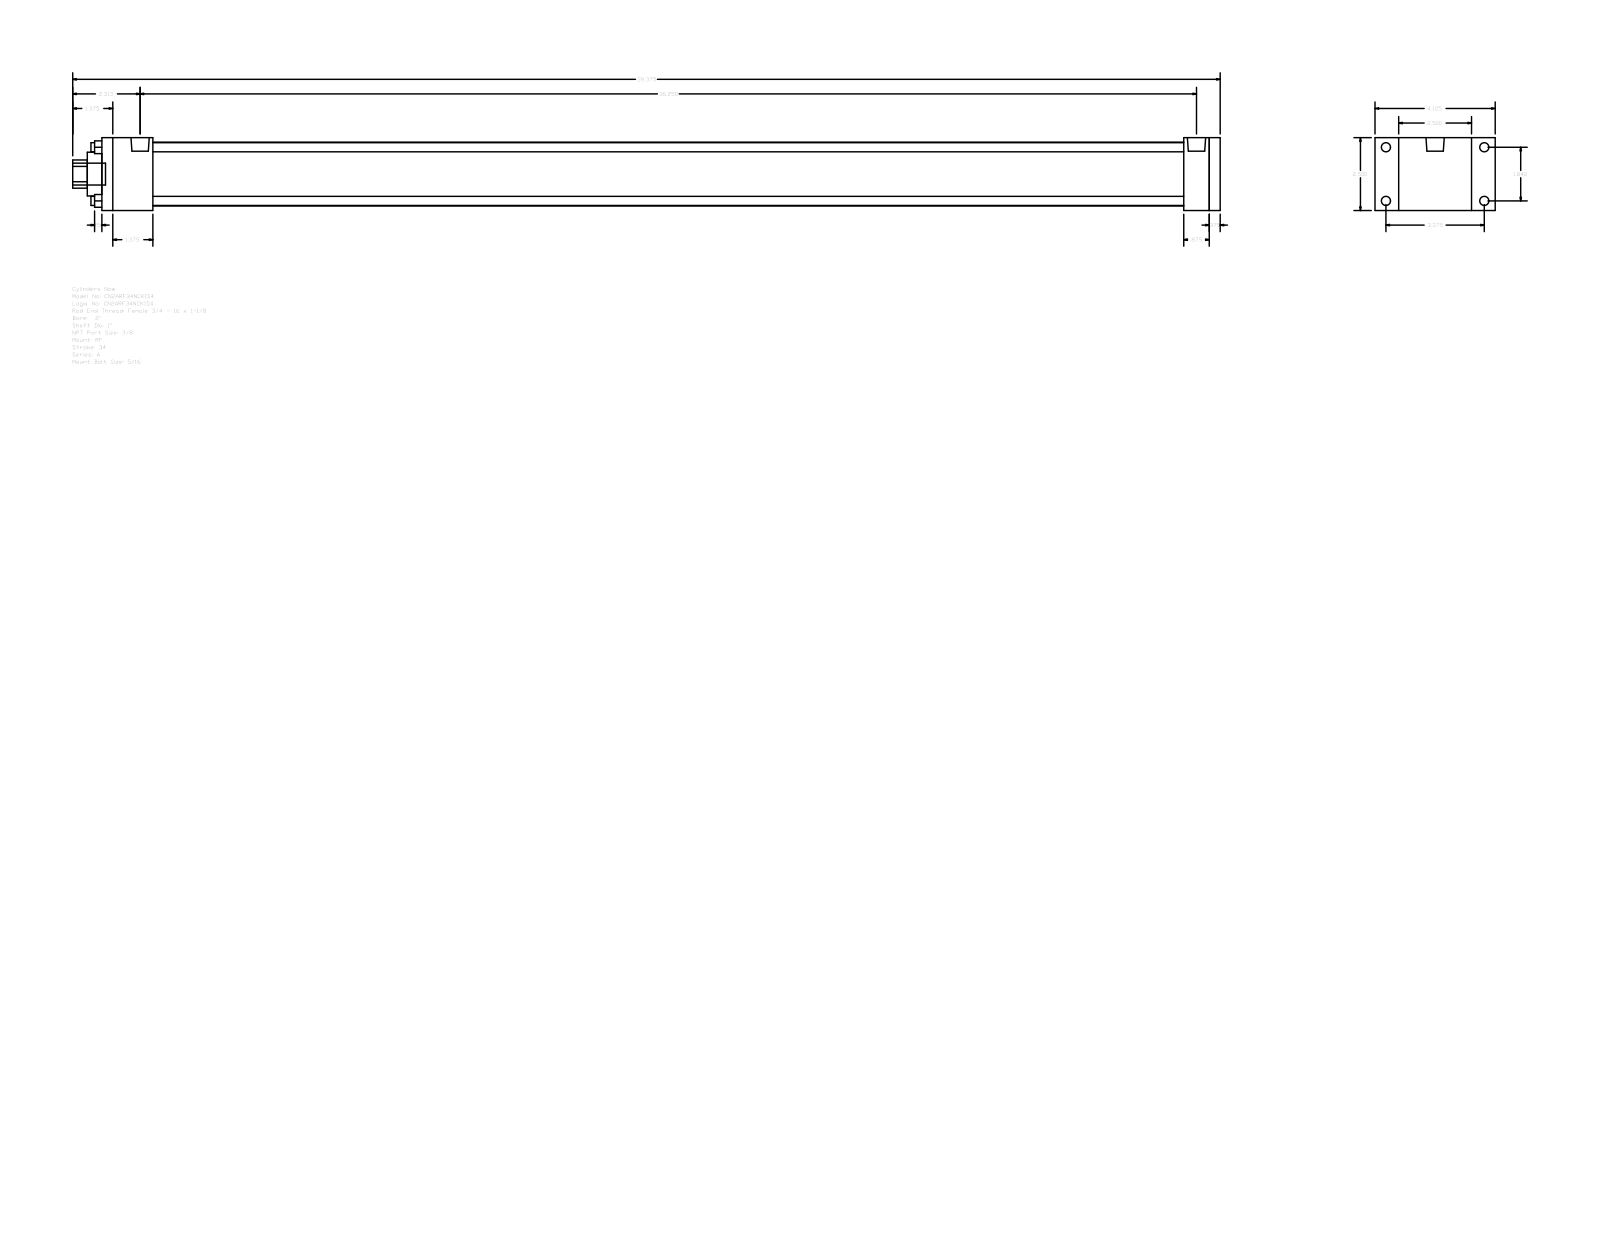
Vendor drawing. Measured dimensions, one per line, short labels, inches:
name: A_RF__0200_1
written by: GSSL Pune (CONFIG_CONTROL_DESIGN)
unit: in
bodies: 0 solids, 92 faces (64 planar, 28 cylindrical, 0 other)
size: 39.375 × 4.125 × 2.5
holes: 4× ⌀0.313, 1× ⌀1, 1× ⌀1.5, 1× ⌀2.19
bosses: 4× ⌀0.313, 4× ⌀0.219, 2× ⌀0.627, 1× ⌀0.75
rounds: 1× R0.484
face distances: 2.5, 0.375, 38.375, 38, 0.813, 1.75, 36.25, 36.625, 37.125, 35.375
hole spacings: 1.301, 1.84, 2.602
